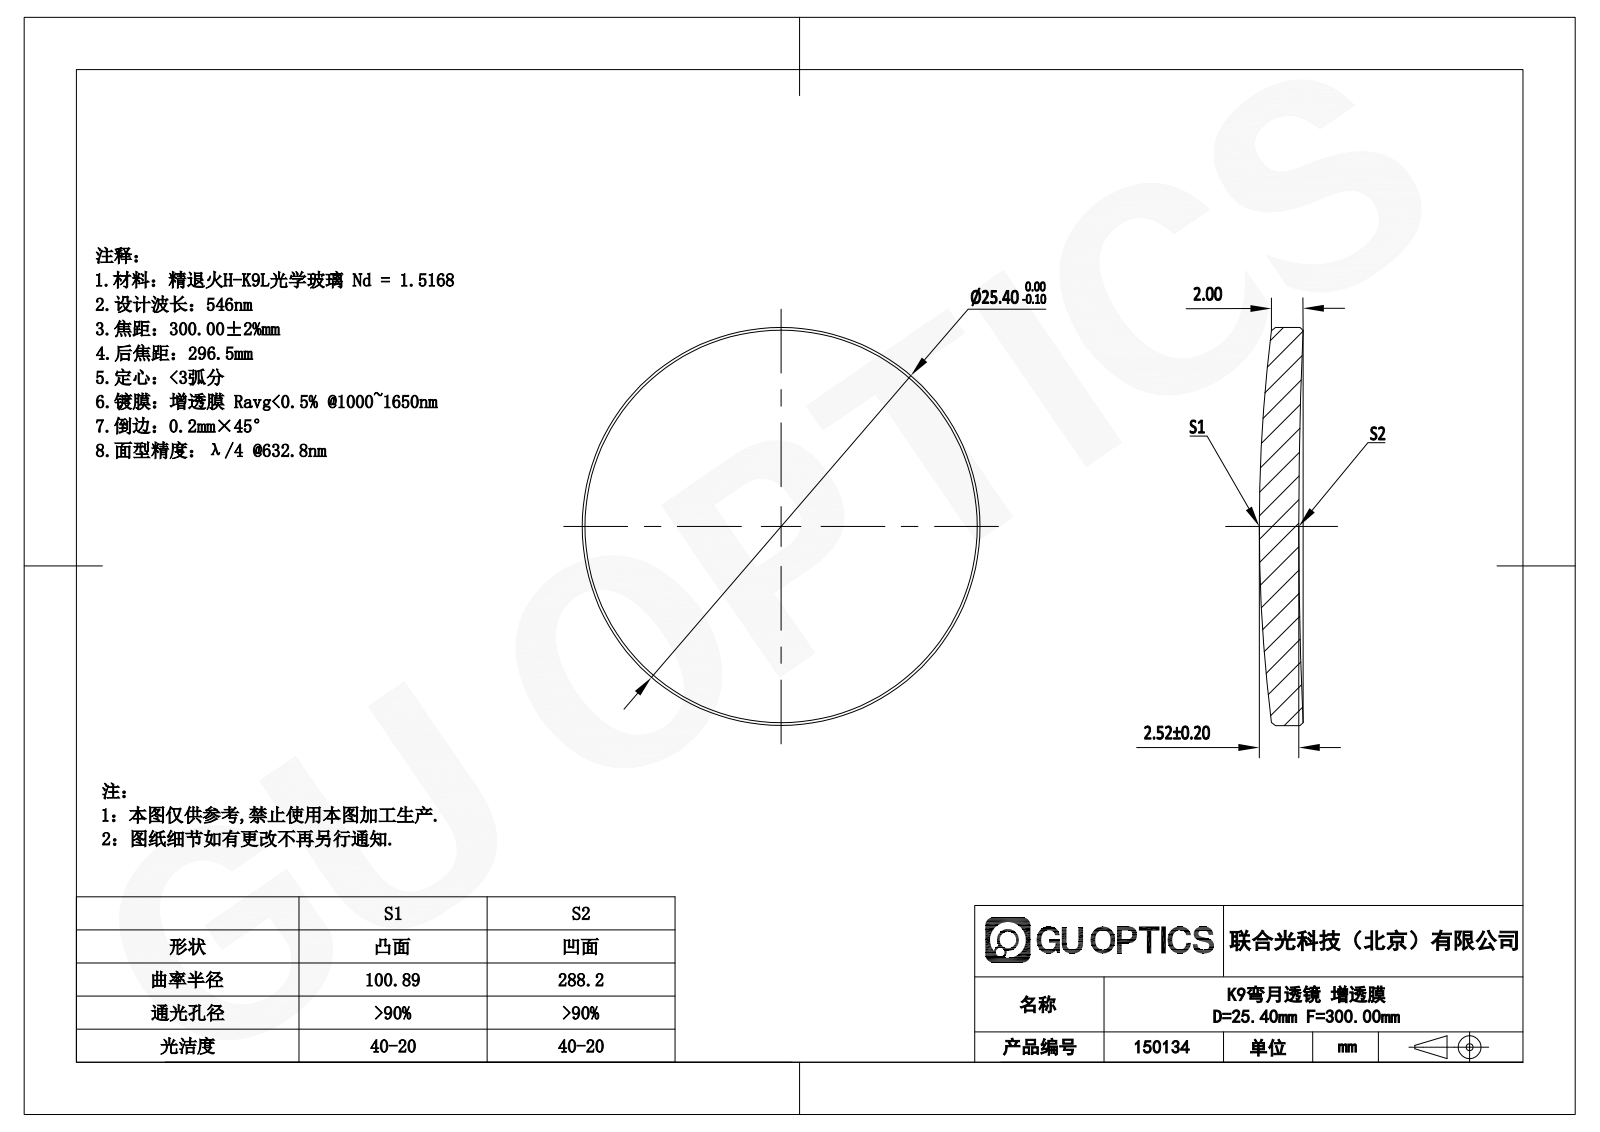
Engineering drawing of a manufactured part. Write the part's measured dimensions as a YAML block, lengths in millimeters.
part_name: "GLM1-025B-300-SWIR"
step_written_by: "SolidWorks 2022 (AUTOMOTIVE_DESIGN)"
units: millimeters
bodies: {solids: 1, faces: 10, planar: 0, cylindrical: 2, other: 8}
overall_size: [25.4, 25.4, 2.79]
volume: 1143
surface_area: 1157
round_bosses_or_shafts:
  - {diameter: 25.4, count: 1}
